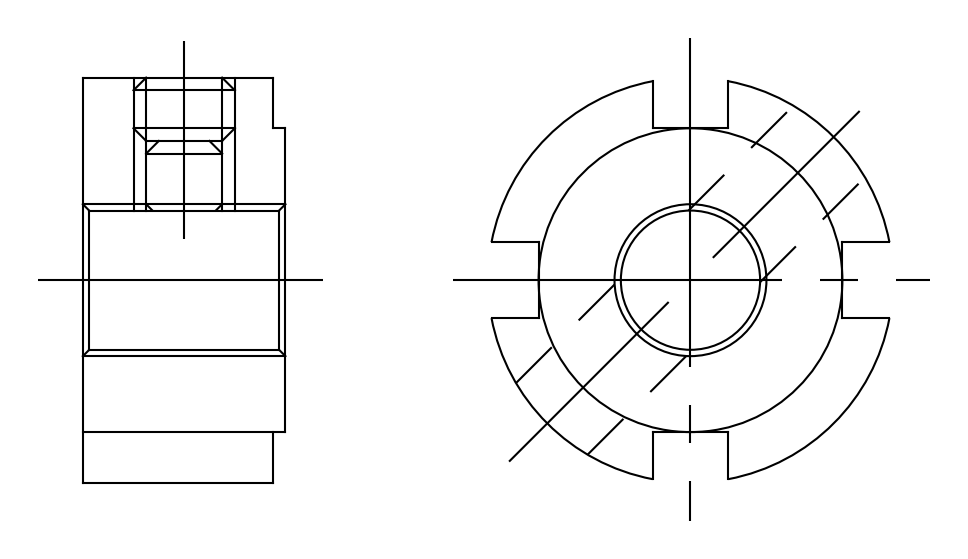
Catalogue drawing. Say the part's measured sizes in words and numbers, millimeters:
The part is named "FKD ZM 6". Its 3-D file was written by "Autodesk Inventor 2011 (AUTOMOTIVE_DESIGN)". It is 1 solid with 26 faces: 18 planar, 8 cylindrical and 0 other. Overall it measures 15.72 by 15.72 by 8 millimeters. Its volume is 1 079 cubic millimeters and its surface area 1 027 square millimeters. Round holes: 2 of diameter 3.24, 1 of diameter 6. Round bosses or shafts: 1 of diameter 12. Partial cylindrical surfaces (rounded edges, fillets, slot ends): 1 of radius 8. The main face-to-face distances are 7.5, 4.5, 8, 0.5, 3, 12.
